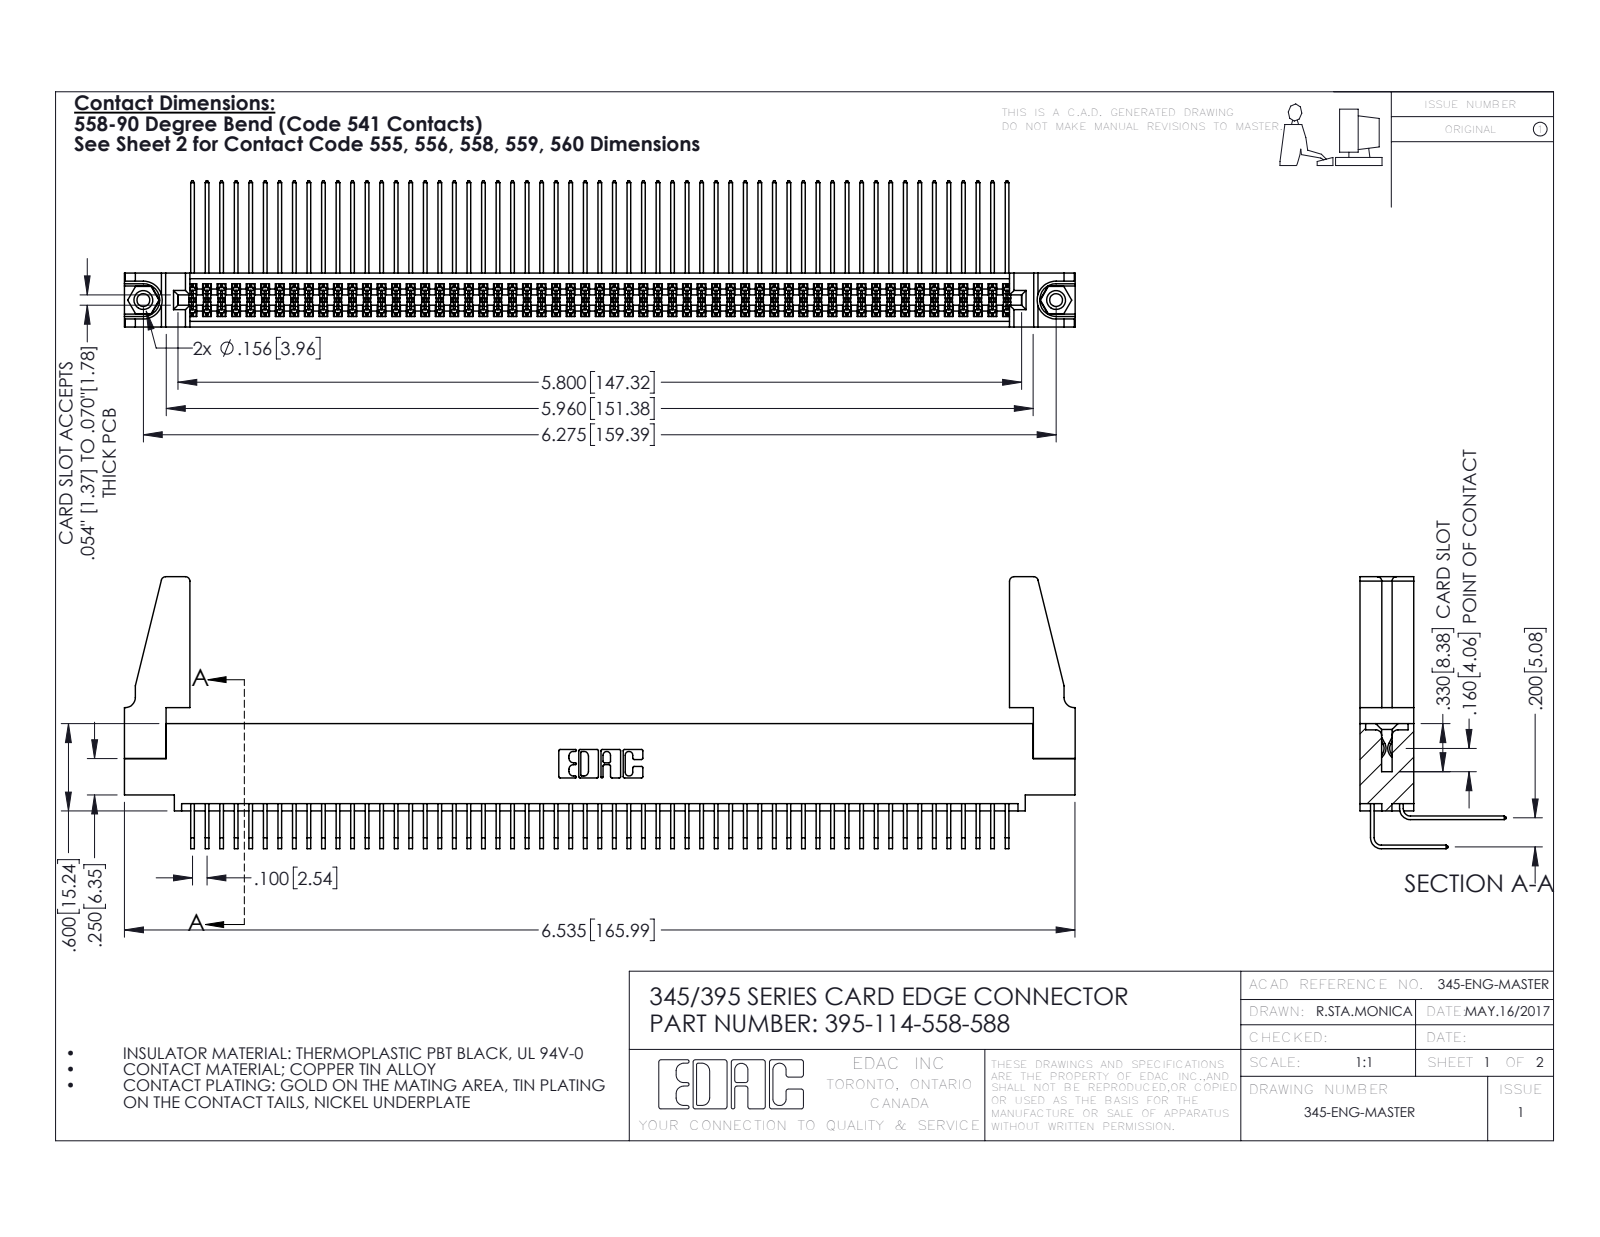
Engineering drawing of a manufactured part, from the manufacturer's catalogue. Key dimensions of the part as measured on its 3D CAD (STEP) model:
Part name (STEP PRODUCT): 345-292-001_558 559 Tail - 1; 345-292-001_558 Tail - 2; 345-250-001_345-250-001-102; 345 Part_0.110 Offset - 0.156 Dia-TH (+2 more)
STEP written by: SolidWorks 2016 (CONFIG_CONTROL_DESIGN)
Units: inches
Bodies: 119 solids, 6182 faces (4146 planar, 2020 cylindrical, 16 other)
Overall size (bounding box): 6.536 × 1.869 × 1.005
Volume: 1.227 in³ · Surface area: 48.83 in²
Round holes (diameter × count): ⌀0.089 ×2, ⌀0.125 ×2, ⌀0.156 ×2, ⌀0.064 ×1
Round bosses / shafts (diameter × count): ⌀0.155 ×2
Partial cylindrical surfaces — rounded edges, fillets, slot ends (radius × count): R0.006 ×172, R0.01 ×22, R0.03 ×8, R0.007 ×6, R0.031 ×6, R0.026 ×3, R0.014 ×2, R0.019 ×2
Main face-to-face distances: 0.072, 0.298, 0.2, 0.37, 0.098, 0.272, 0.025, 0.225, 0.025, 0.175
Hole centre spacings: 0.27, 6.039, 6.275
